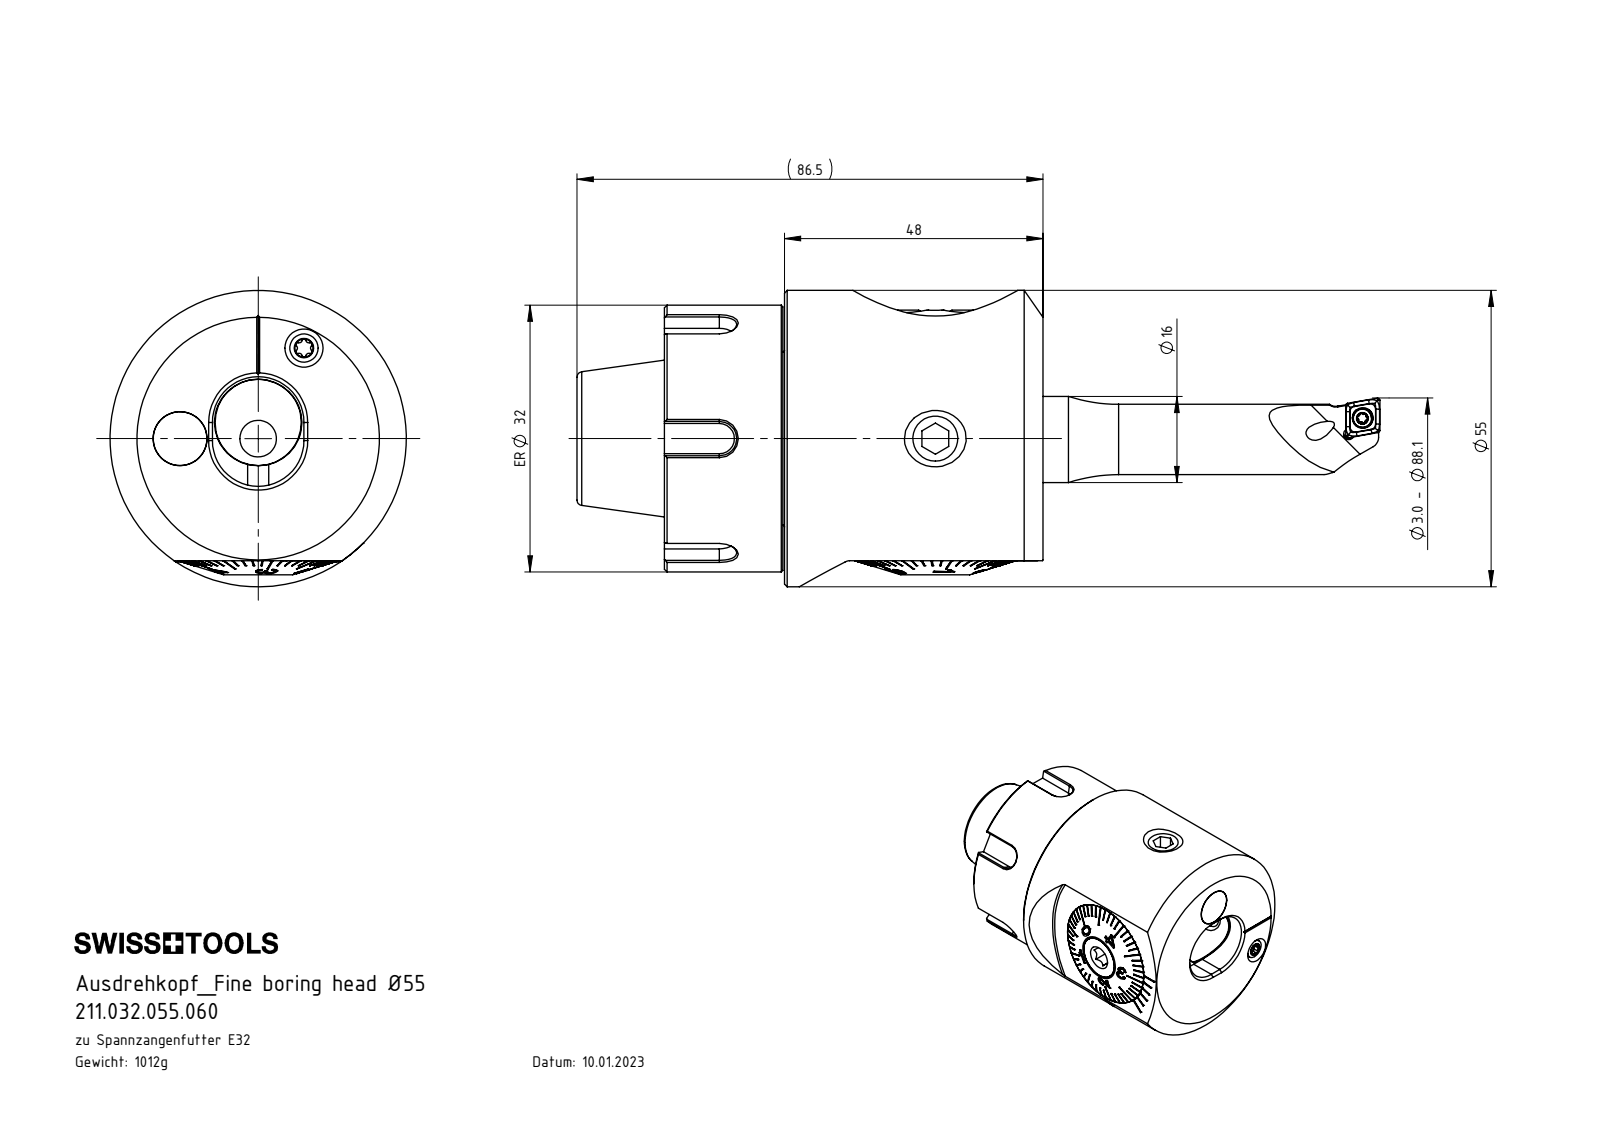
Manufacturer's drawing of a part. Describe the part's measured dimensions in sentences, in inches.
The part is named "DIN 3771 - 25x1.5; MSX-ER1.XXX.XXX_A_Mutter Spannzangenkegel E32; A55-BG2.013.005_C; A55-BG1.011.041_E (+8 more)". Its 3-D file was written by "SolidWorks 2017 (CONFIG_CONTROL_DESIGN)". It is 22 solids with 1144 faces: 434 planar, 242 cylindrical and 468 other. Overall it measures 9.404 by 2.48 by 2.48 inches. Its volume is 17.64 cubic inches and its surface area 138.5 square inches. Round holes: 3 of diameter 0.315, 3 of diameter 0.335, 2 of diameter 0.079, 2 of diameter 0.118, 2 of diameter 0.197, 2 of diameter 0.394, 1 of diameter 0.039, 1 of diameter 0.063, 1 of diameter 0.081, 1 of diameter 0.11, 1 of diameter 0.13, 1 of diameter 0.152. Round bosses or shafts: 4 of diameter 0.394, 1 of diameter 2.48, 1 of diameter 2.165, 1 of diameter 2.163, 1 of diameter 1.949, 1 of diameter 1.887, 1 of diameter 1.772, 1 of diameter 1.26. Partial cylindrical surfaces (rounded edges, fillets, slot ends): 6 of radius 0.008, 6 of radius 0.013, 6 of radius 0.023, 6 of radius 0.055, 5 of radius 0.014, 5 of radius 0.315, 4 of radius 0.113, 3 of radius 0.126. The main face-to-face distances are 0.02, 0.63, 3.898, 3.878, 5.787, 1.909, 1.89, 0.866, 1.99, 0.209. The hole center spacings are 0.285, 0.571, 3.545, 0.153, 0.157, 0.579, 0.741, 0.813.
